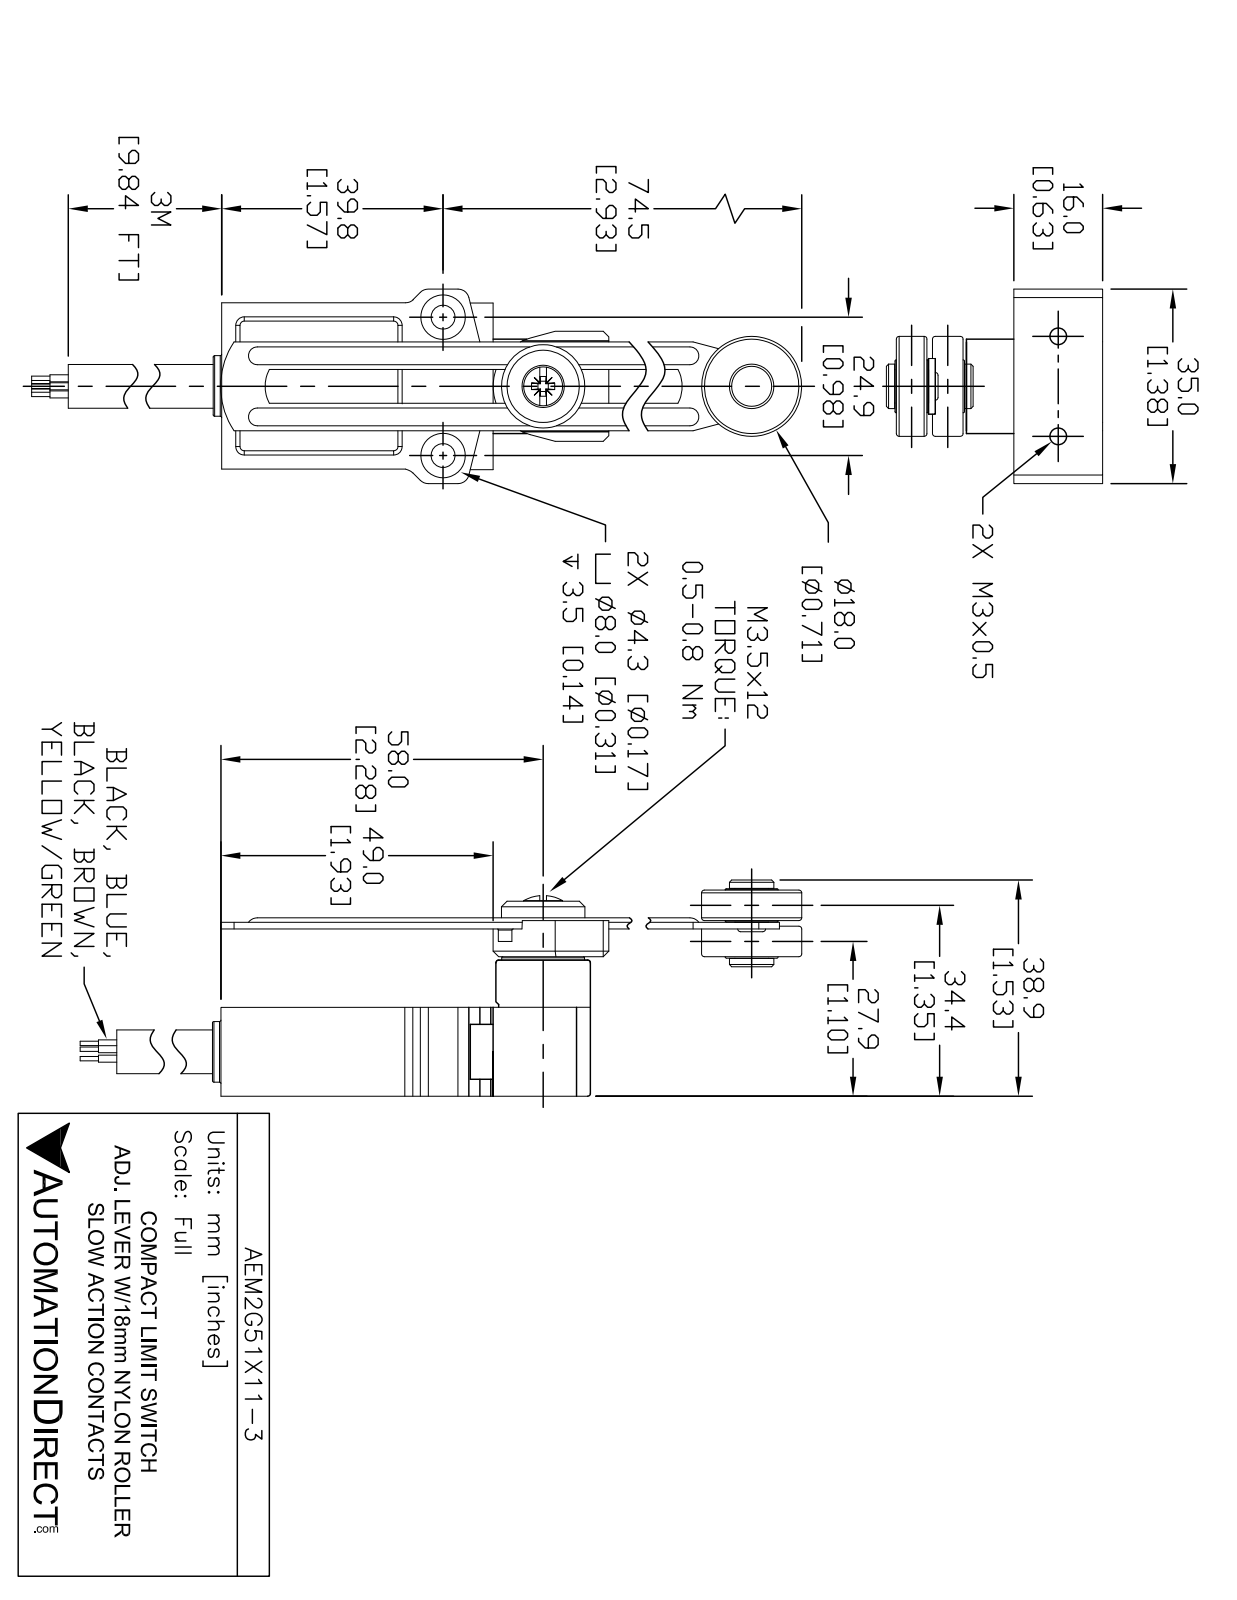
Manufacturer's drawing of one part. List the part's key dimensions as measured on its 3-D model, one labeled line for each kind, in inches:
Part name (STEP PRODUCT): AEM2G51X11-3_Default
STEP written by: SolidWorks 2021 (CONFIG_CONTROL_DESIGN)
Units: inches
Bodies: 4 solids, 194 faces (98 planar, 75 cylindrical, 21 other)
Overall size (bounding box): 5.008 × 1.544 × 1.378
Volume: 2.052 in³ · Surface area: 22.03 in²
Round holes (diameter × count): ⌀0.118 ×2, ⌀0.173 ×2, ⌀0.323 ×2, ⌀0.197 ×1, ⌀0.3 ×1
Round bosses / shafts (diameter × count): ⌀0.276 ×2, ⌀0.71 ×1, ⌀0.622 ×1, ⌀0.59 ×1, ⌀0.371 ×1, ⌀0.288 ×1, ⌀0.238 ×1, ⌀0.213 ×1
Partial cylindrical surfaces — rounded edges, fillets, slot ends (radius × count): R0.079 ×8, R0.01 ×4, R0.043 ×4, R0.06 ×4, R0.084 ×4, R0.052 ×2, R0.255 ×1, R0.256 ×1
Main face-to-face distances: 0.63, 0.554, 1.184, 0.25, 1.181, 0.05, 0.604, 1.234, 0.354, 0.2
Hole centre spacings: 0.863, 0.748, 0.984
